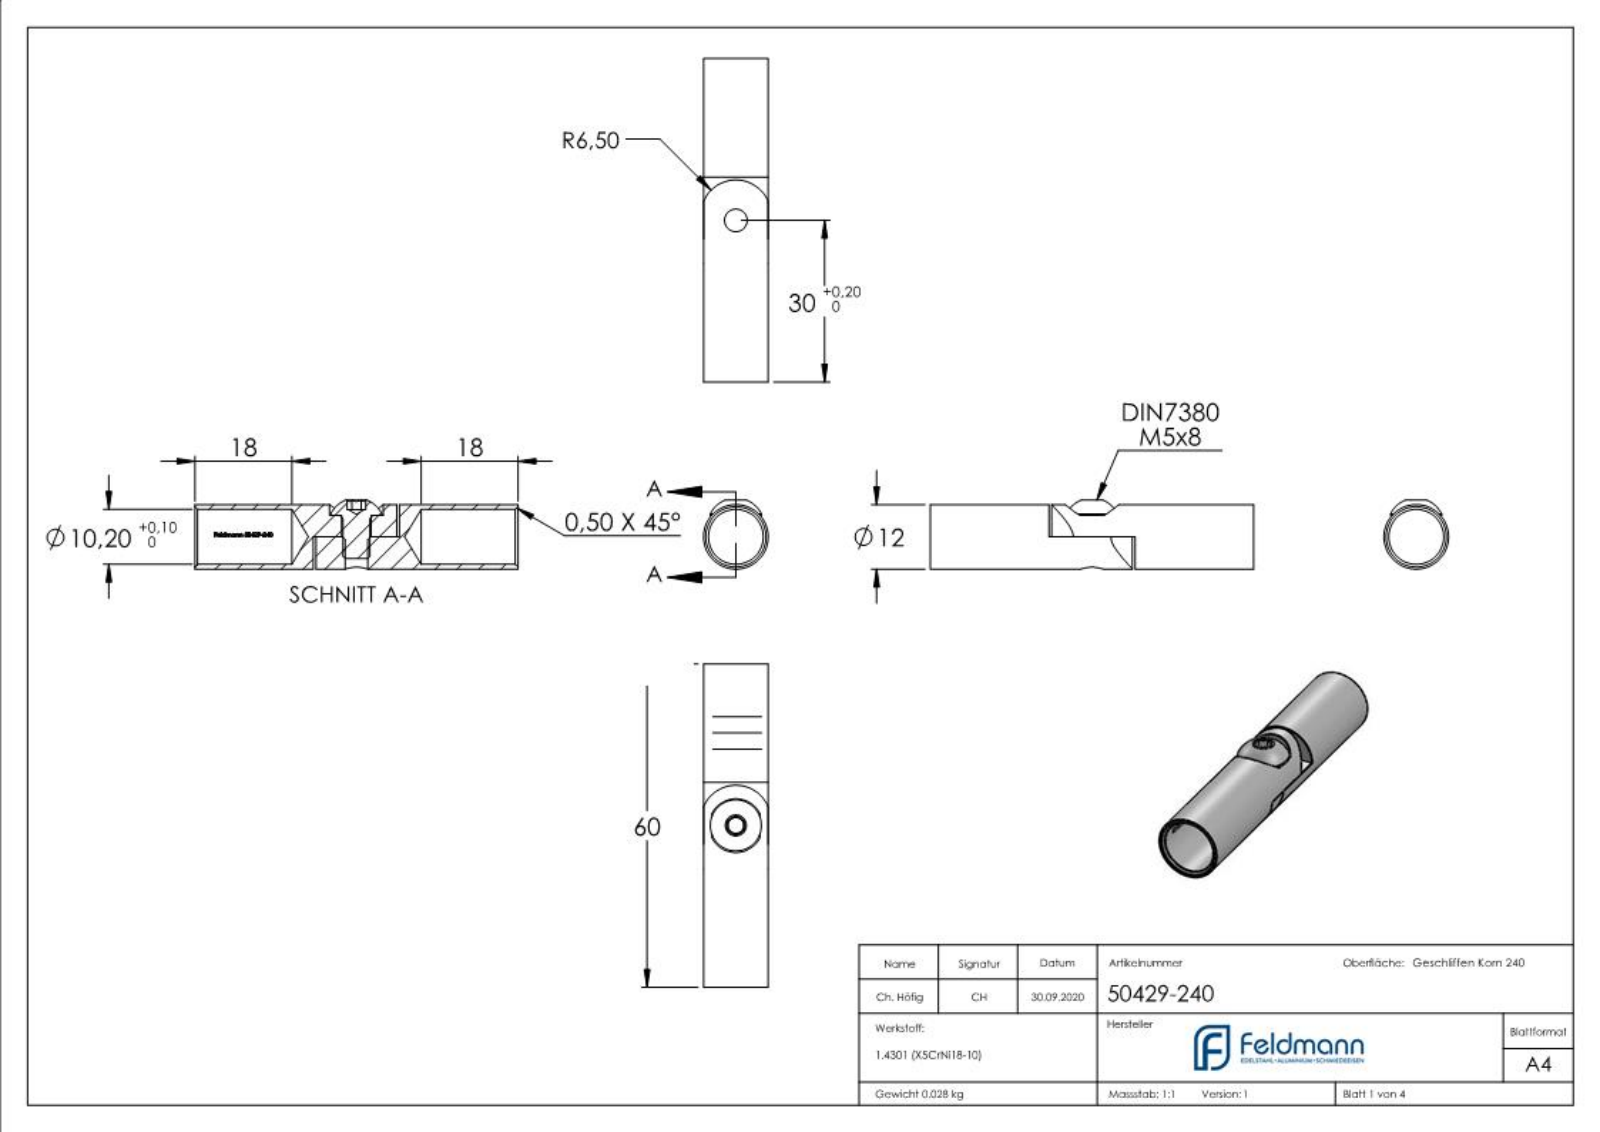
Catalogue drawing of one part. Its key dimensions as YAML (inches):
part_name: "504XX-240 Teil1; 50429-240; DIN 7380; 504XX-240 Teil2_50429-240 Teil2 (+3 more)"
step_written_by: "SolidWorks 2018 (CONFIG_CONTROL_DESIGN)"
units: inches
bodies: {solids: 3, faces: 290, planar: 122, cylindrical: 48, other: 120}
overall_size: [2.362, 0.504, 0.472]
volume: 0.214
surface_area: 7.066
round_holes:
  - {diameter: 0.165, count: 1}
  - {diameter: 0.217, count: 1}
  - {diameter: 0.402, count: 1}
round_bosses_or_shafts:
  - {diameter: 0.472, count: 1}
  - {diameter: 0.374, count: 1}
  - {diameter: 0.197, count: 1}
partial_cylinders:
  - {radius: 0.256, count: 2}
  - {radius: 0.197, count: 1}
  - {radius: 0.205, count: 1}
face_to_face_distances: [0.157, 0.63, 0.866, 1.496, 2.362, 0.315, 0.118, 0.425, 0.268, 0.11]
